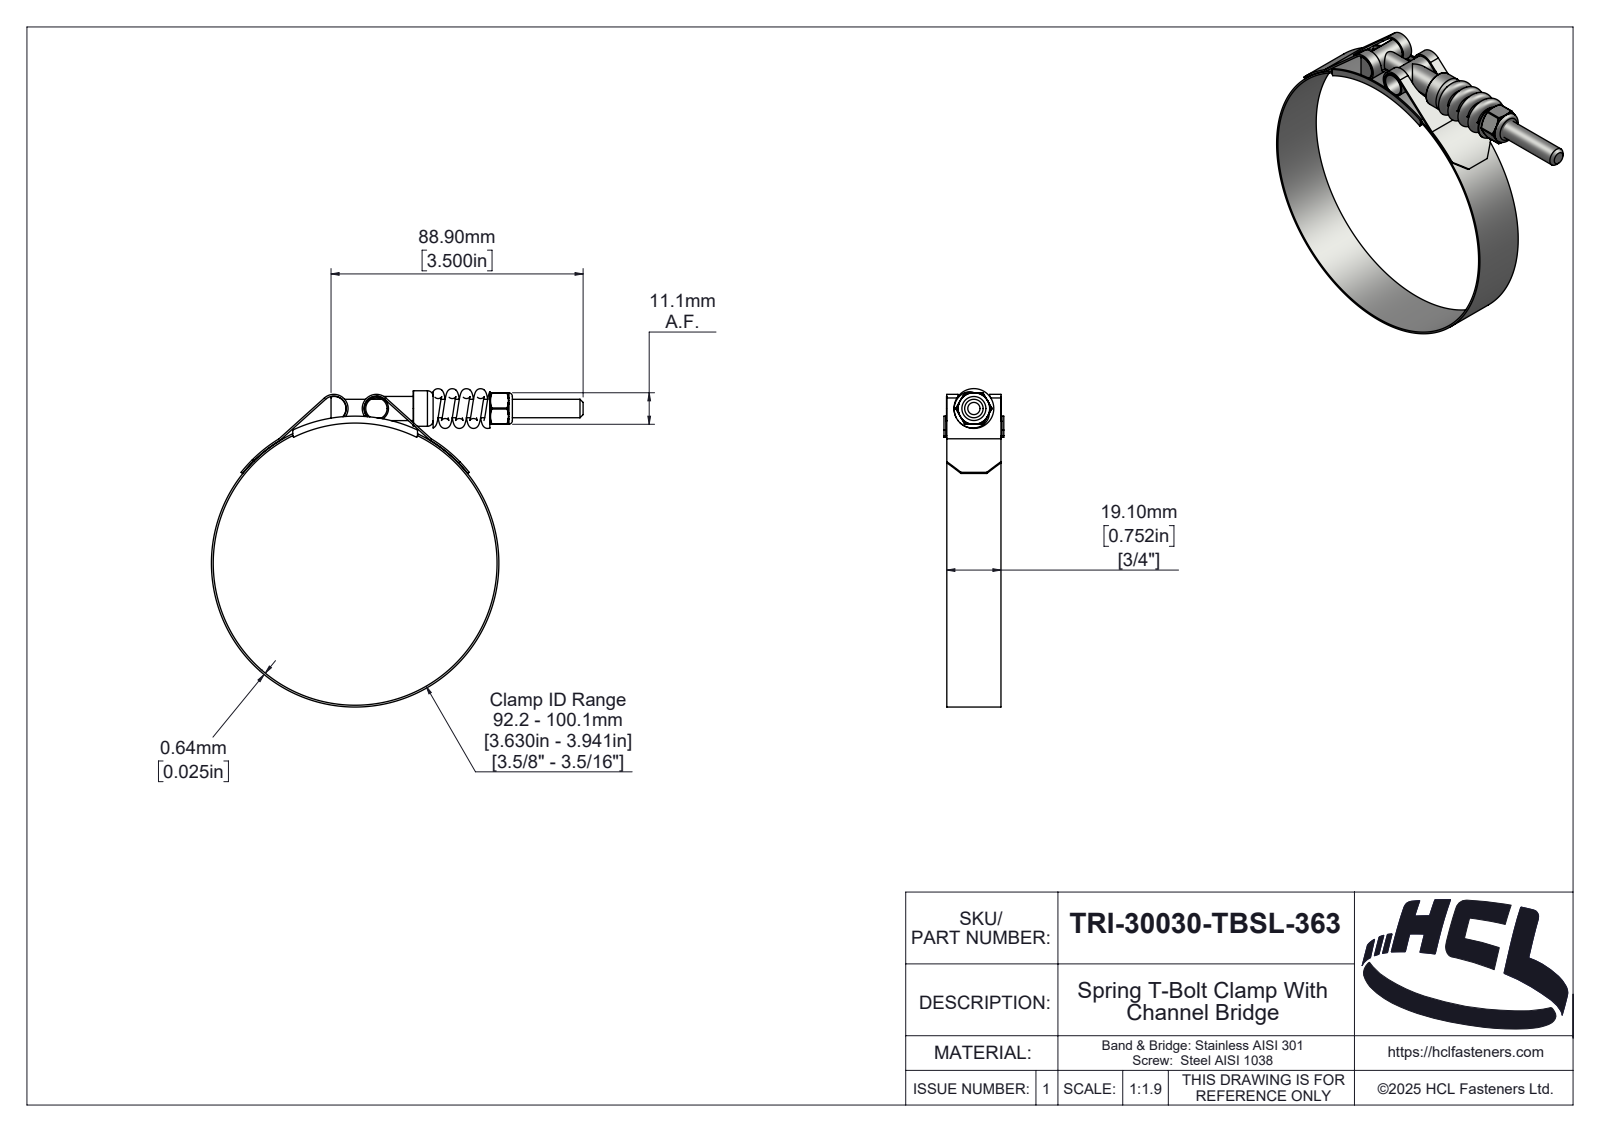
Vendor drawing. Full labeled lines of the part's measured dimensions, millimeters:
Part name (STEP PRODUCT): TRI-30030-TBSL-363
STEP written by: SolidWorks 2025 (AUTOMOTIVE_DESIGN)
Units: millimetres
Bodies: 7 solids, 332 faces (48 planar, 122 cylindrical, 162 other)
Overall size (bounding box): 132.09 × 112.25 × 21.1
Volume: 11 871 mm³ · Surface area: 24 280 mm²
Round holes (diameter × count): ⌀5.4 ×1, ⌀6.35 ×1, ⌀6.5 ×1, ⌀7.52 ×1, ⌀100.1 ×1
Round bosses / shafts (diameter × count): ⌀8.52 ×2, ⌀101.38 ×1, ⌀12.52 ×1
Partial cylindrical surfaces — rounded edges, fillets, slot ends (radius × count): R0.39 ×6, R0.5 ×2, R4.36 ×2, R5 ×2, R0.59 ×1, R2.42 ×1, R3.03 ×1, R3.19 ×1
Main face-to-face distances: 0.64, 19.1, 1, 20.1, 20.46, 0.36, 19.46, 56, 21.1, 11.11
Hole centre spacings: 55.05
